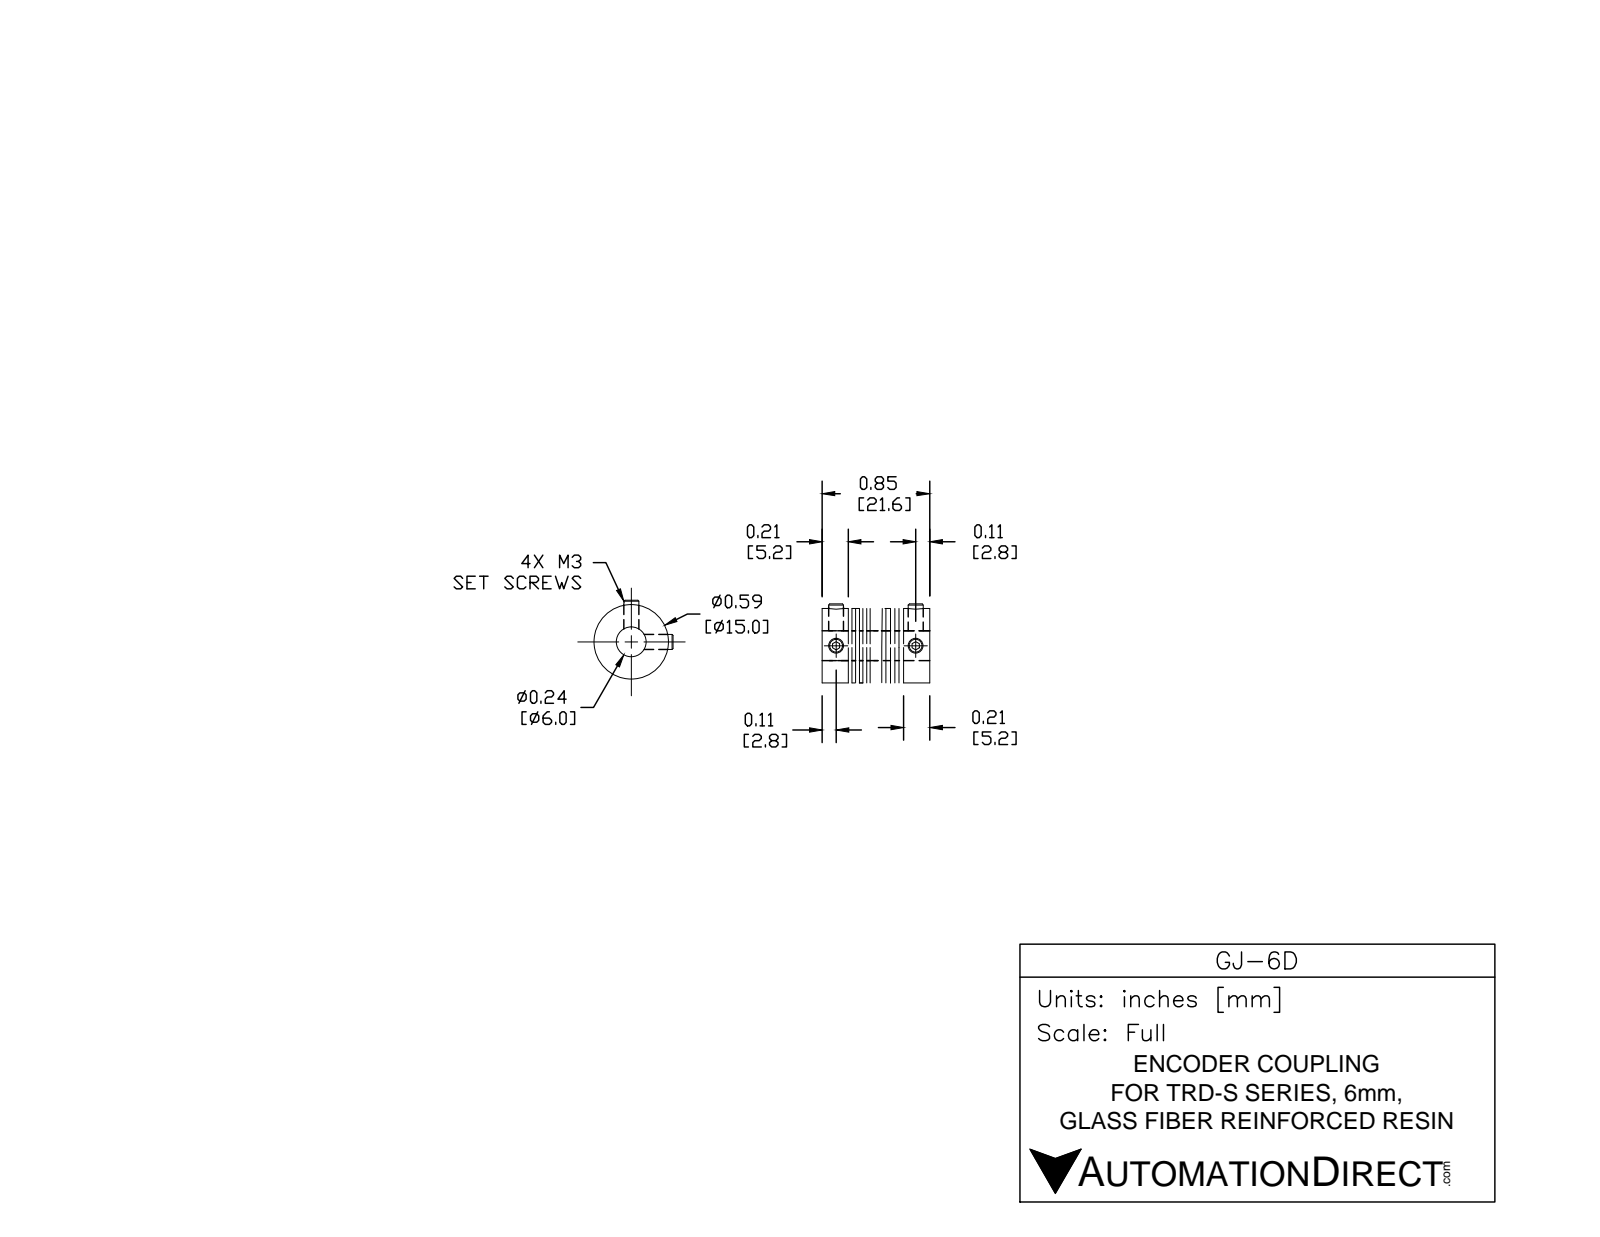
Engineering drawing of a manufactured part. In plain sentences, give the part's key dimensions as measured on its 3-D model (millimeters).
The part is named "GJ-6D". Its 3-D file was written by "SolidWorks 2016 (AUTOMOTIVE_DESIGN)". It is 1 solid with 146 faces: 94 planar, 20 cylindrical and 32 other. Overall it measures 22 by 15 by 15 millimeters. Its volume is 2 436 cubic millimeters and its surface area 2 920 square millimeters. Round holes: 4 of diameter 2.5, 1 of diameter 6. Round bosses or shafts: 1 of diameter 15. The main face-to-face distances are 5.2, 2.6, 7.8, 1.2, 6.4, 9, 10.4, 3.8, 1.4, 4. The hole center spacings are 16.
